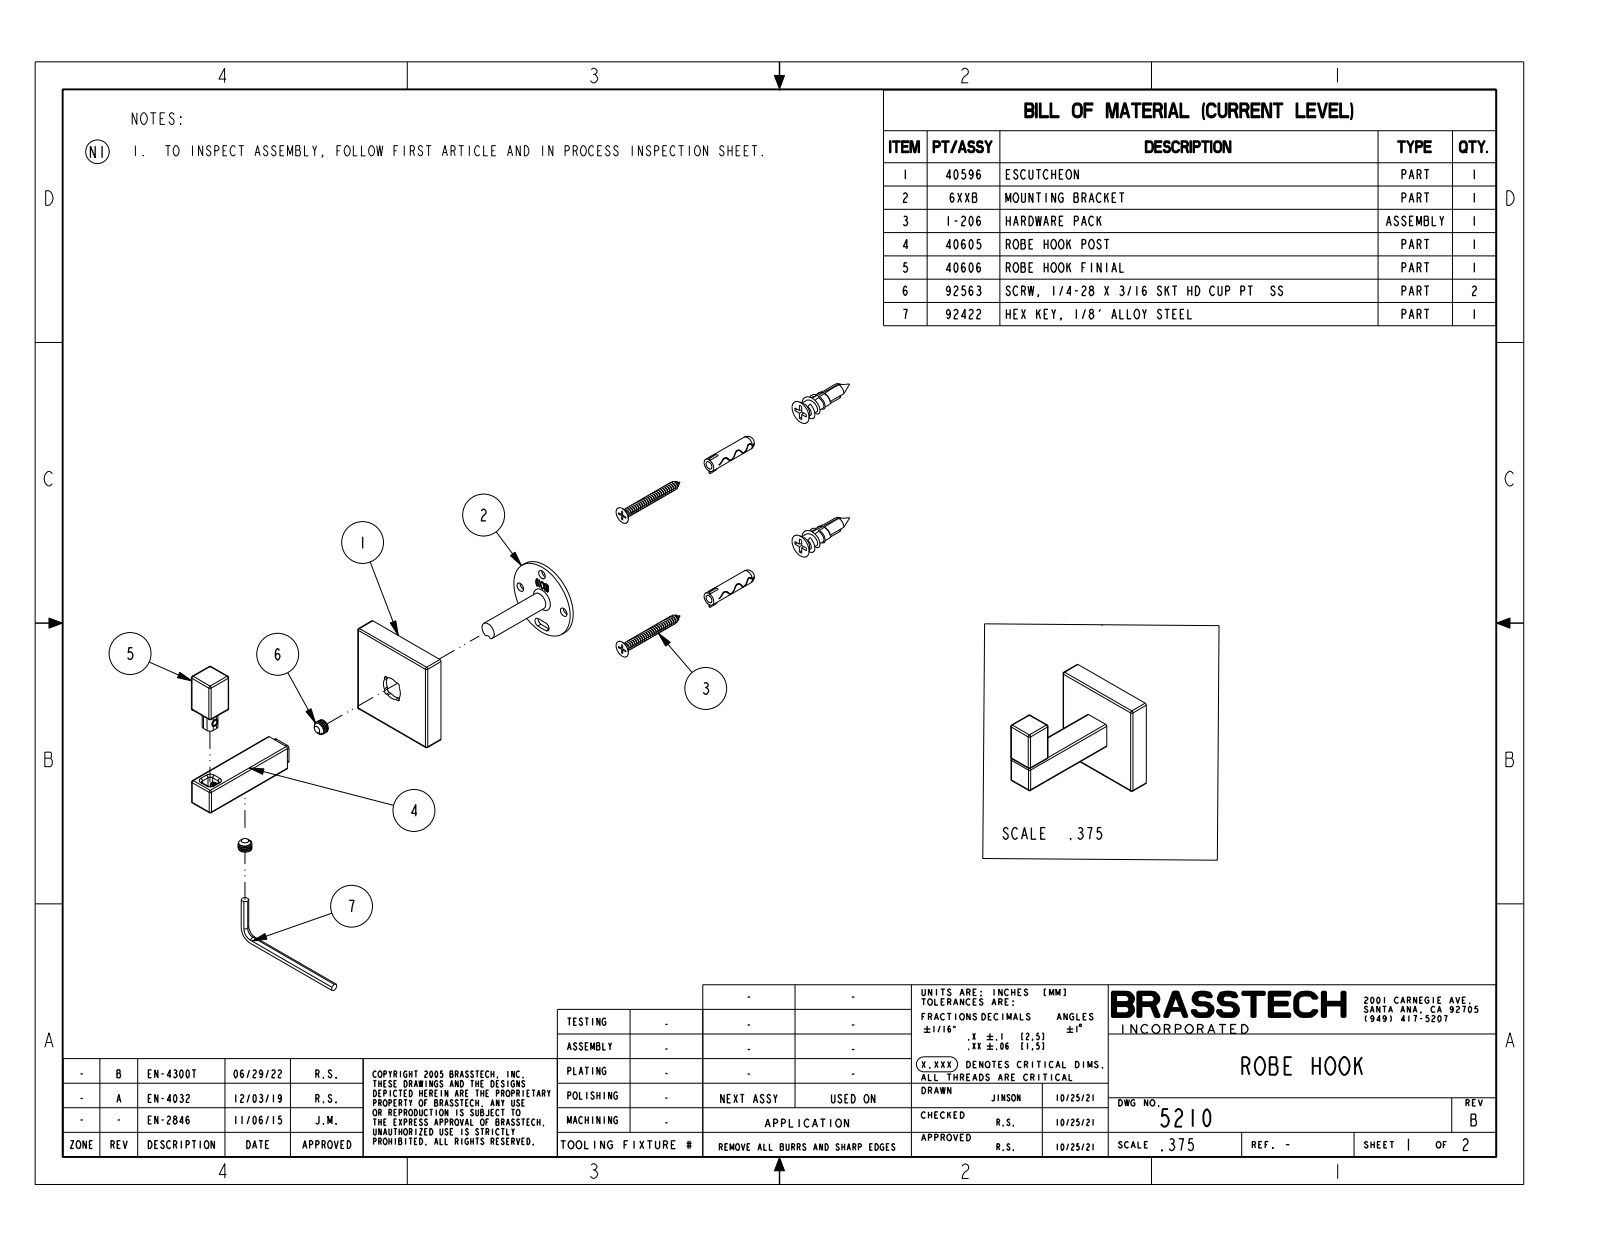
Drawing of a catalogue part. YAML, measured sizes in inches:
part_name: "40596; 6XXB; 40605; 40606 (+2 more)"
step_written_by: "PRO/ENGINEER BY PARAMETRIC TECHNOLOGY CORPORATION, 2013150 (CONFIG_CONTROL_DESIGN)"
units: inches
bodies: {solids: 7, faces: 521, planar: 250, cylindrical: 157, other: 114}
overall_size: [2.38, 1.9, 1.8]
volume: 1.199
surface_area: 37.86
round_holes:
  - {diameter: 0.169, count: 3}
  - {diameter: 0.213, count: 2}
  - {diameter: 0.323, count: 1}
round_bosses_or_shafts:
  - {diameter: 0.25, count: 2}
  - {diameter: 1.46, count: 1}
  - {diameter: 0.315, count: 1}
partial_cylinders:
  - {radius: 0.03, count: 36}
  - {radius: 0.05, count: 8}
  - {radius: 0.06, count: 4}
  - {radius: 0.08, count: 4}
  - {radius: 0.01, count: 2}
  - {radius: 0.085, count: 2}
  - {radius: 0.158, count: 1}
  - {radius: 0.22, count: 1}
face_to_face_distances: [1.15, 0.65, 0.5, 0.078, 1.8, 0.375, 0.297, 1.072, 1.722, 0.572]
hole_center_spacings: [0.563, 0.796, 1.126]
